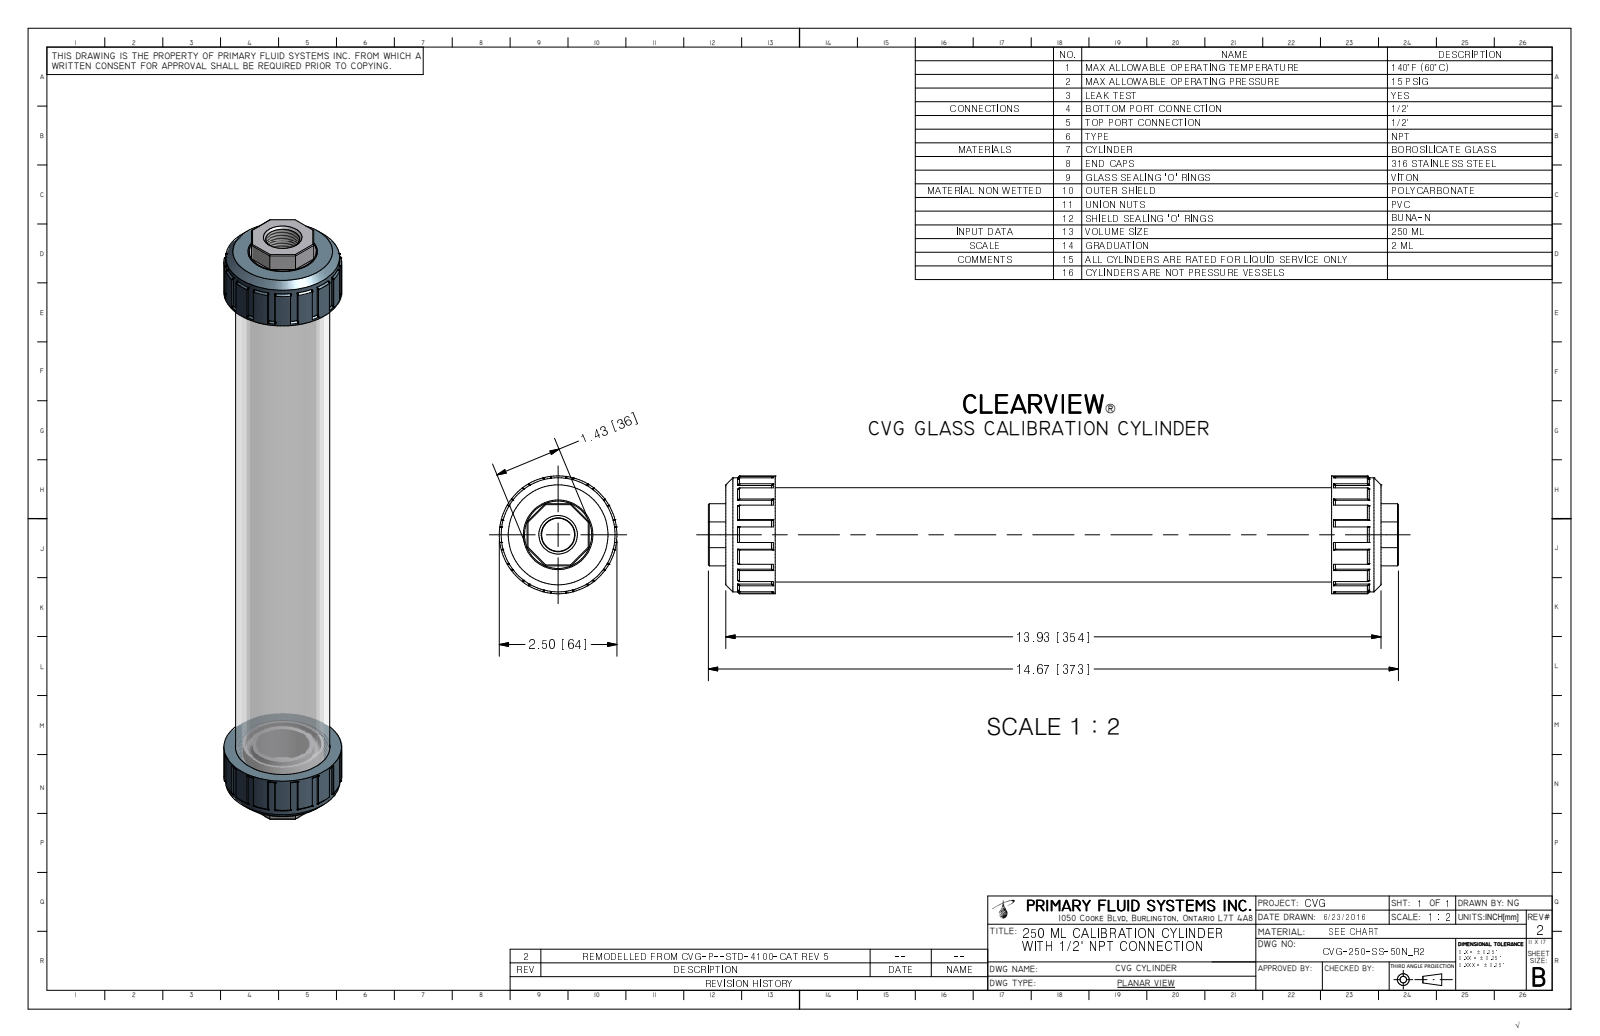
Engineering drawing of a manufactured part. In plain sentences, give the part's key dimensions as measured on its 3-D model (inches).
The part is named "CVG-250-SS-50N_R2; CVG-3-250-METAL-NPT-50_R4; CVG-1-250-A_R0; CVG-6-250_R0 (+1 more)". Its 3-D file was written by "Autodesk Inventor 2009 (AUTOMOTIVE_DESIGN)". It is 6 solids with 308 faces: 91 planar, 35 cylindrical and 182 other. Overall it measures 14.67 by 2.5 by 2.5 inches. Its volume is 20.62 cubic inches and its surface area 351 square inches. Round holes: 1 of diameter 0.719, 1 of diameter 1.14, 1 of diameter 1.417, 1 of diameter 1.635, 1 of diameter 1.75. Round bosses or shafts: 1 of diameter 2.5, 1 of diameter 2, 1 of diameter 1.921, 1 of diameter 1.86, 1 of diameter 1.725, 1 of diameter 1.591, 1 of diameter 1.575, 1 of diameter 1.43. The main face-to-face distances are 0.82, 12.65, 11.83, 0.6, 1.42, 13.25, 14.07, 0.869, 13.801, 0.269.
